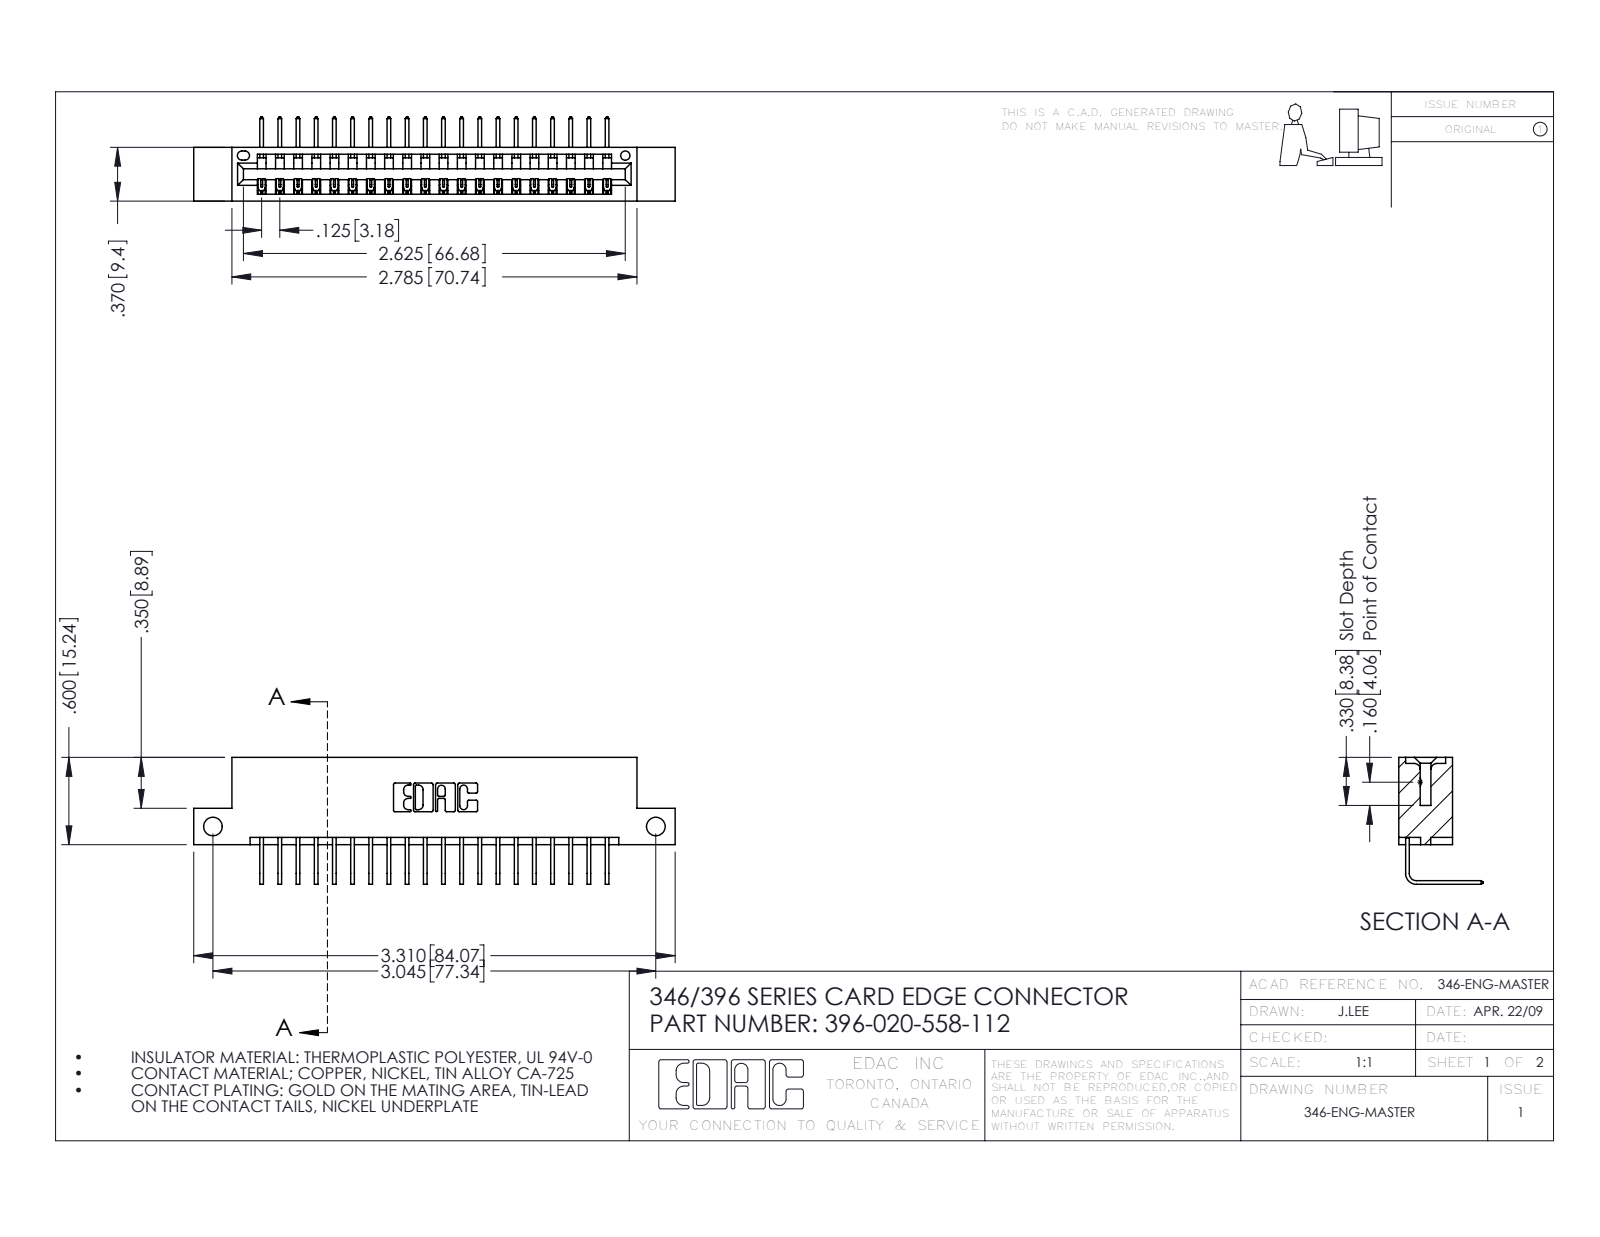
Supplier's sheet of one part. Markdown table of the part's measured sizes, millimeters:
| quantity | value |
| --- | --- |
| part name | 396-020-558-112; 346 Part_Flush Mounting Lugs - Side Mount; 345-292-001_558 Tail - 2 |
| STEP written by | SolidWorks 2016 (CONFIG_CONTROL_DESIGN) |
| units | millimeters |
| bodies | 21 solids, 1322 faces (916 planar, 406 cylindrical, 0 other) |
| overall size | 84.1 × 22.2 × 14.7 |
| volume | 7 880 mm³ |
| surface area | 9 858 mm² |
| round holes (diameter × count) | 3.3 × 2, 1.6 × 1 |
| partial cylindrical surfaces (radius × count) | 0.2 × 40, 0.3 × 22, 0.2 × 6, 0.8 × 6, 0.7 × 3, 0.8 × 2, 1 × 2, 0.4 × 1 |
| main face-to-face distances | 8.2, 1.2, 6.4, 9.4, 7.6, 0.6, 1.8, 3.8, 5.6, 2.5 |
| hole center spacings | 77.3 |
